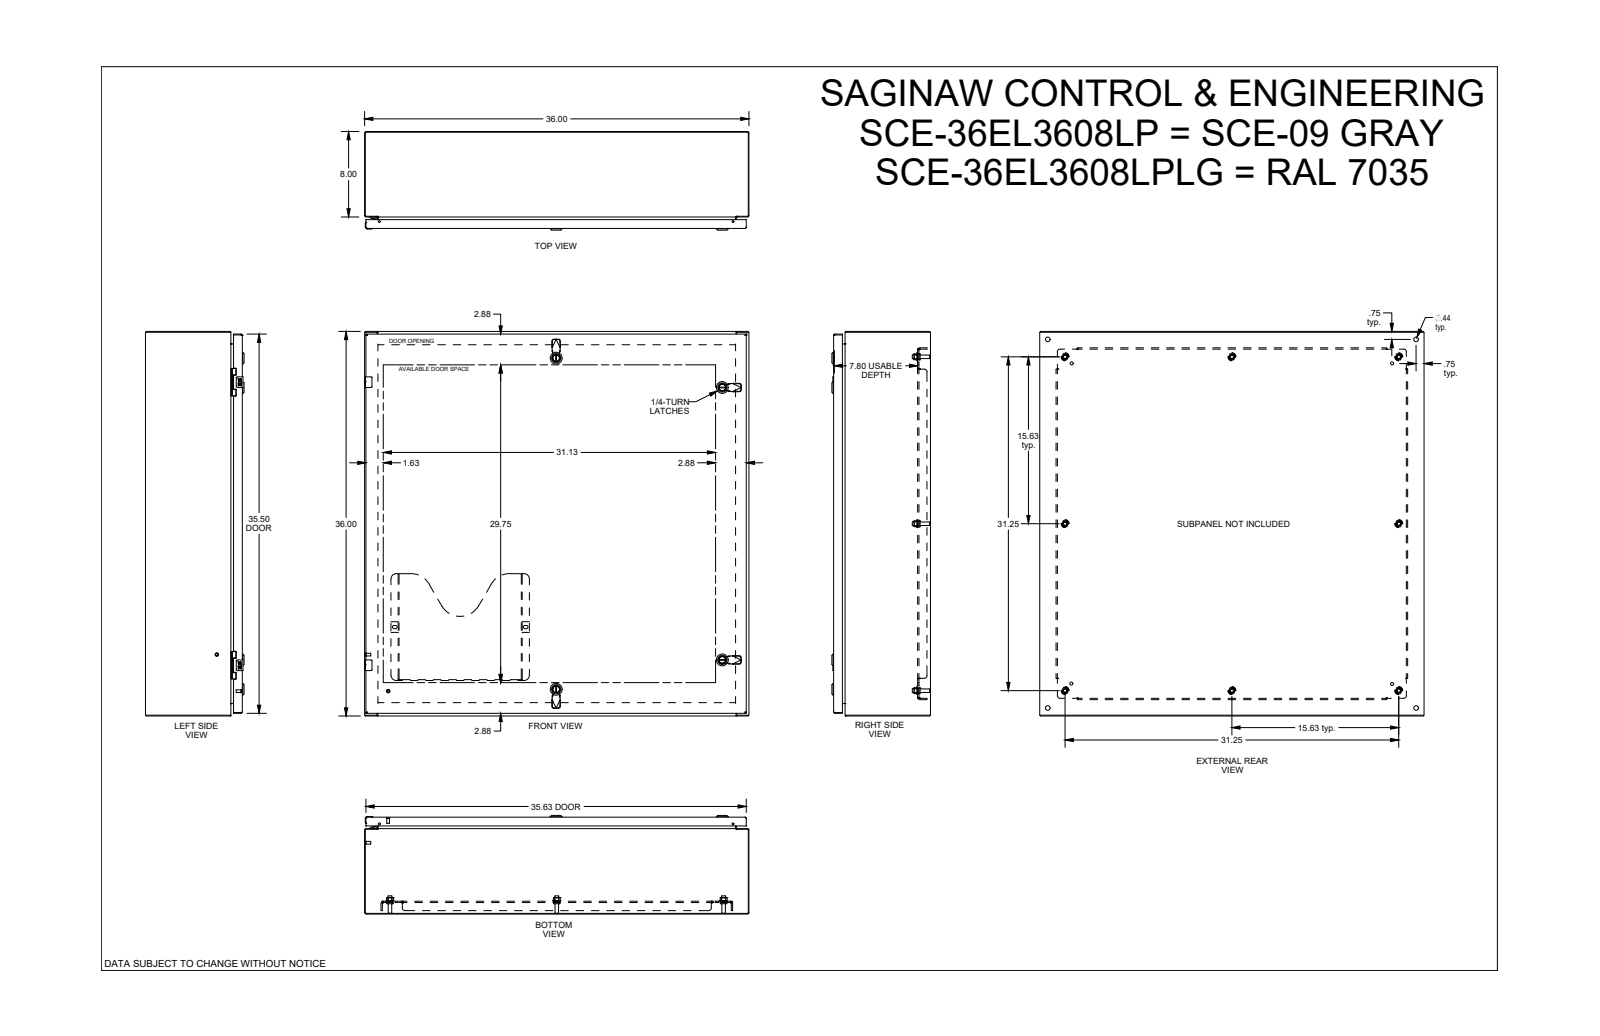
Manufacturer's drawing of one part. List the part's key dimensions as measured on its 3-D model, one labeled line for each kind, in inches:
Part name (STEP PRODUCT): SCE-36EL3608LP
STEP written by: SolidWorks 2021 (AUTOMOTIVE_DESIGN)
Units: inches
Bodies: 65 solids, 3849 faces (1489 planar, 1198 cylindrical, 1162 other)
Overall size (bounding box): 36 × 36 × 9.23
Volume: 476 in³ · Surface area: 11 180 in²
Round holes (diameter × count): ⌀0.367 ×8, ⌀0.5 ×8, ⌀0.172 ×4, ⌀0.197 ×4, ⌀0.205 ×4, ⌀0.244 ×4, ⌀0.266 ×4, ⌀0.281 ×4, ⌀0.315 ×4, ⌀0.375 ×4, ⌀0.394 ×4, ⌀0.437 ×4
Round bosses / shafts (diameter × count): ⌀0.366 ×8, ⌀0.332 ×8, ⌀0.17 ×6, ⌀1.102 ×4, ⌀0.78 ×4, ⌀0.63 ×4, ⌀0.531 ×4, ⌀0.504 ×4
Partial cylindrical surfaces — rounded edges, fillets, slot ends (radius × count): R0.012 ×110, R0.01 ×52, R0.02 ×44, R0.015 ×20, R0.04 ×17, R0.157 ×16, R0.06 ×13, R0.029 ×12
Main face-to-face distances: 0.075, 0.06, 0.075, 9.073, 8.998, 9.013, 8.938, 1.2, 7.873, 35.925
Hole centre spacings: 17.326, 37.126, 0.985, 15.019, 26.5, 32.334, 34.11, 0.02
